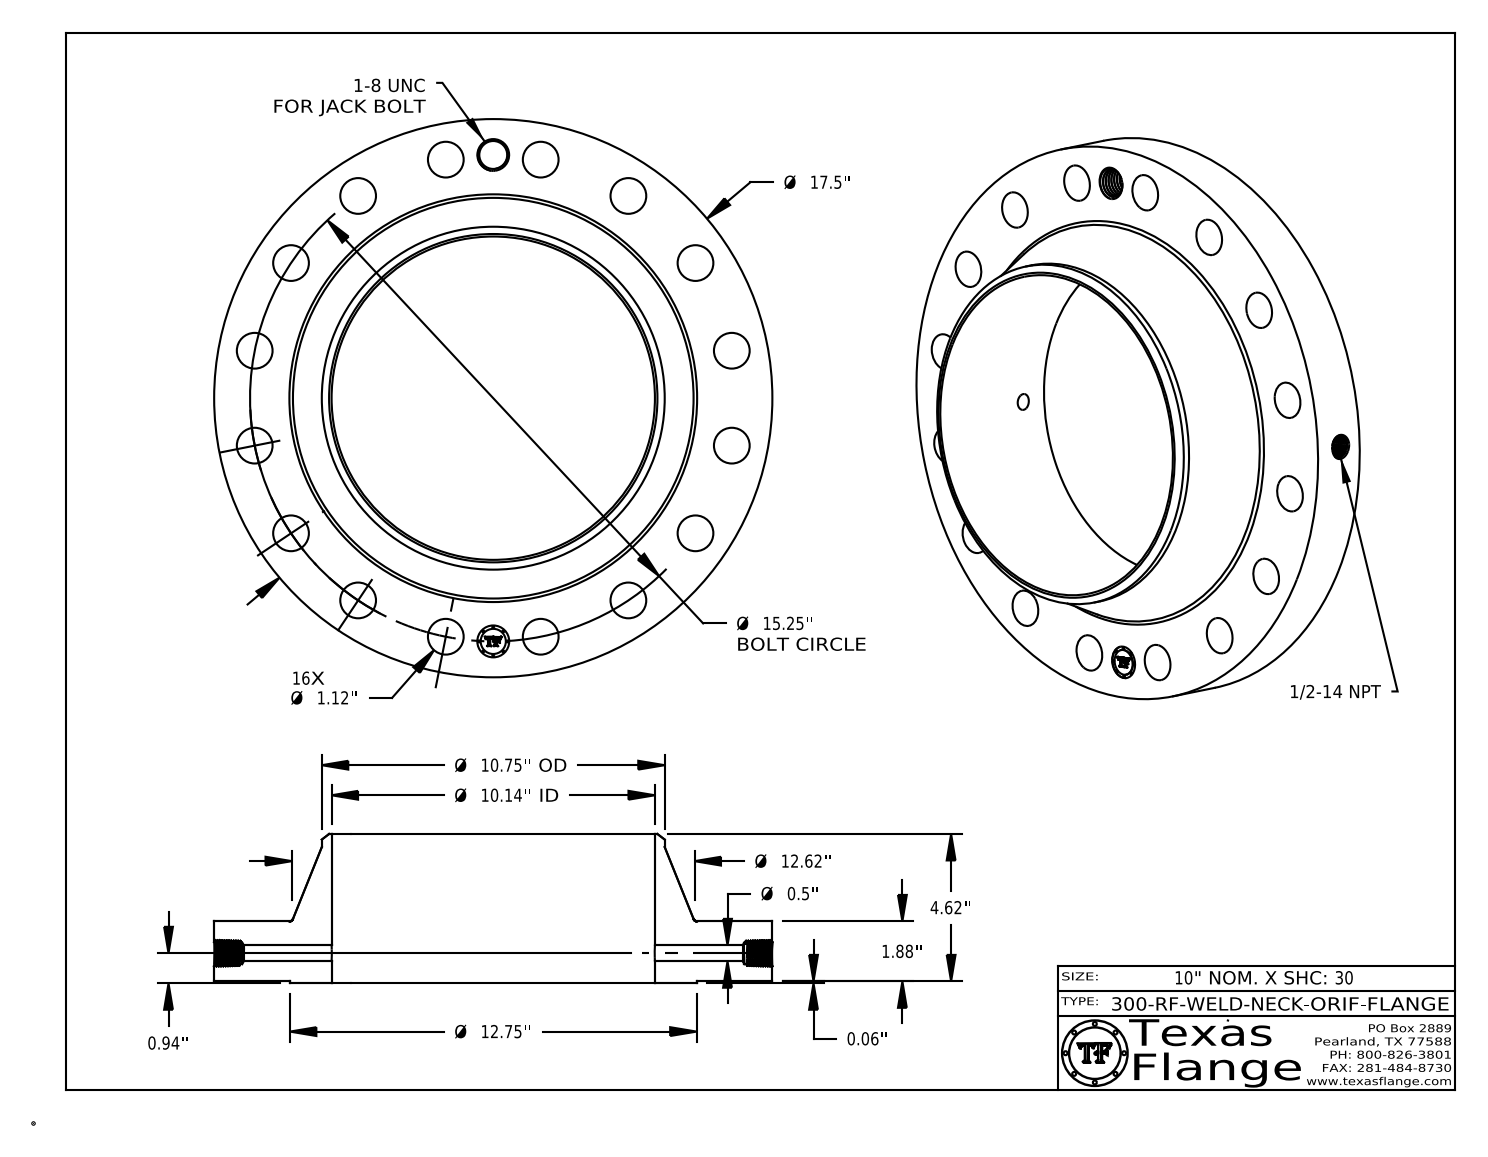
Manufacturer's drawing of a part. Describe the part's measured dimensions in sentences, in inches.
The part is named "300-RF-WELD-NECK". Its 3-D file was written by "CATIA V5 STEP AP214 (AUTOMOTIVE_DESIGN)". It is 1 solid with 787 faces: 369 planar, 109 cylindrical and 309 other. Overall it measures 17.5 by 17.5 by 4.68 inches. Its volume is 336.4 cubic inches and its surface area 737.2 square inches. Round holes: 16 of diameter 1.12, 1 of diameter 0.5, 1 of diameter 0.672, 1 of diameter 0.875, 1 of diameter 1, 1 of diameter 10.136. Round bosses or shafts: 8 of diameter 0.061, 1 of diameter 17.5, 1 of diameter 12.75, 1 of diameter 10.75, 1 of diameter 0.788. The main face-to-face distances are 1.88, 0.06, 1.94, 4.68, 4.62, 2.74, 0.015, 1.925, 1.865, 2.755. The hole center spacings are 5.836, 7.625, 10.783, 14.089, 14.957, 2.975, 2.975, 8.472.
